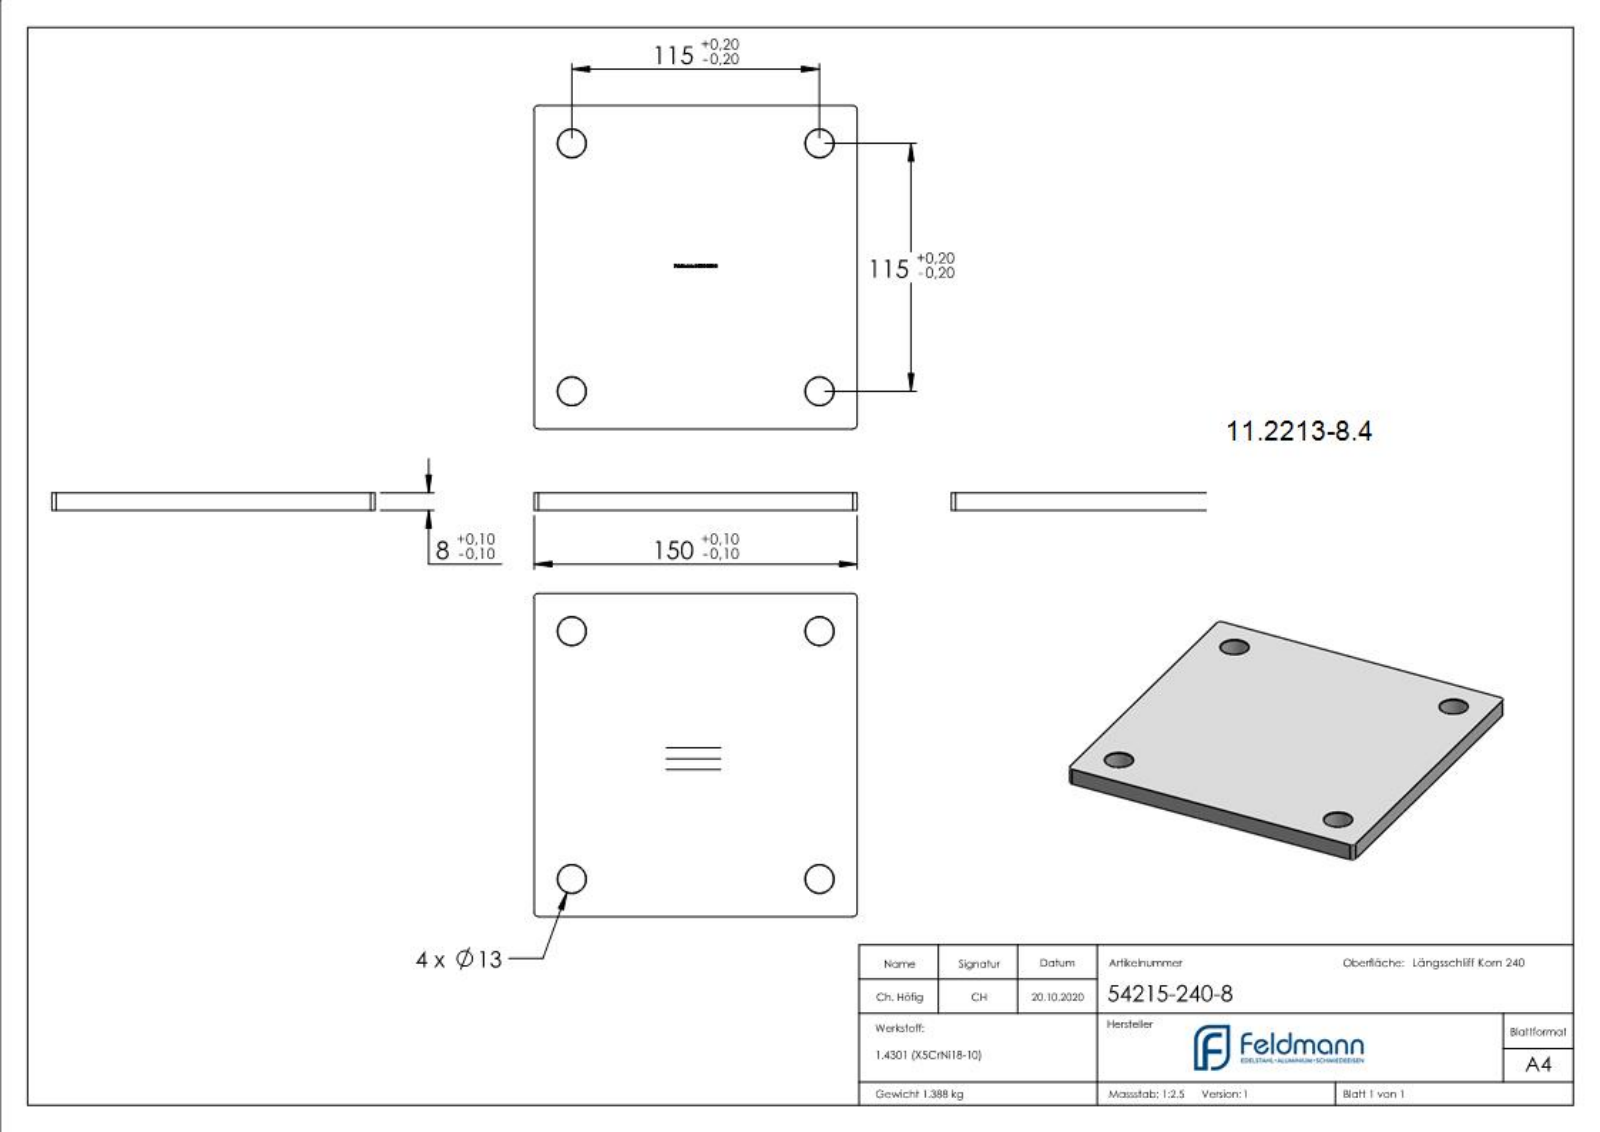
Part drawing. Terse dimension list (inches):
name: 54215-240-8
written by: SolidWorks 2018 (CONFIG_CONTROL_DESIGN)
unit: in
bodies: 1 solid, 281 faces (151 planar, 12 cylindrical, 118 other)
size: 5.906 × 5.906 × 0.315
volume: 10.72 in³; area: 77.46 in²
holes: 4× ⌀0.512
rounds: 4× R0.079
face distances: 0.315, 5.906, 0.311, 2.953, 0.017, 0.035, 0.185, 0.423, 0.052, 0.08
hole spacings: 4.528, 6.403
